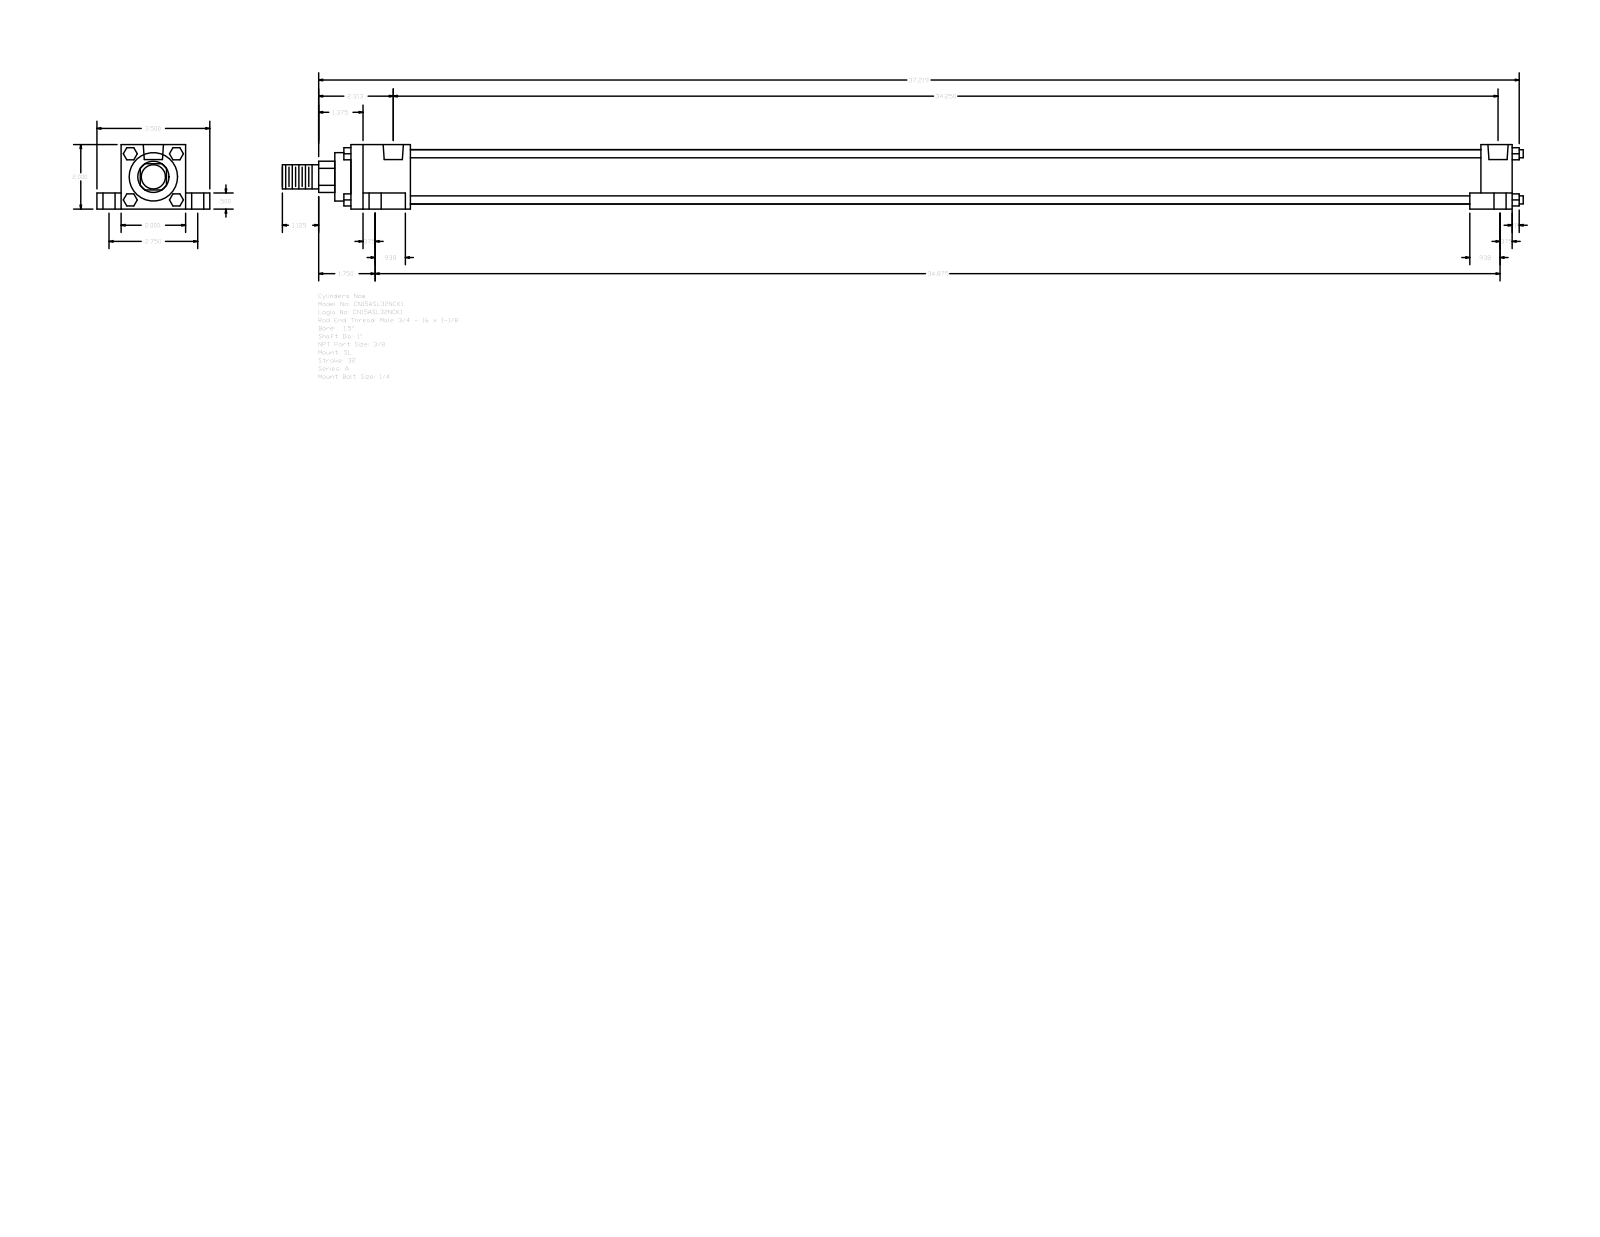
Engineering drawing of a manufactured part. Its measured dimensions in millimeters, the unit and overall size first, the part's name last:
Units: millimetres
Overall size (bounding box): 977.11 × 88.9 × 50.8
Round holes (diameter × count): ⌀5.56 ×4, ⌀9.53 ×4, ⌀15.88 ×4, ⌀15.93 ×2
Round bosses / shafts (diameter × count): ⌀6.35 ×4, ⌀42.93 ×1, ⌀38.1 ×1, ⌀25.4 ×1, ⌀19.05 ×1
Partial cylindrical surfaces — rounded edges, fillets, slot ends (radius × count): R12.29 ×1
Main face-to-face distances: 50.8, 12.7, 38.1, 19.05, 69.85, 9.52, 914.4, 33.34, 889.79, 24.61
Hole centre spacings: 3.97, 34.96, 35.36, 37.73, 39.41, 69.84, 862.01, 865.98
Bodies: 0 solids, 148 faces (112 planar, 36 cylindrical, 0 other)
Part name (STEP PRODUCT): A_SL__0150_1
STEP written by: GSSL Pune (CONFIG_CONTROL_DESIGN)
